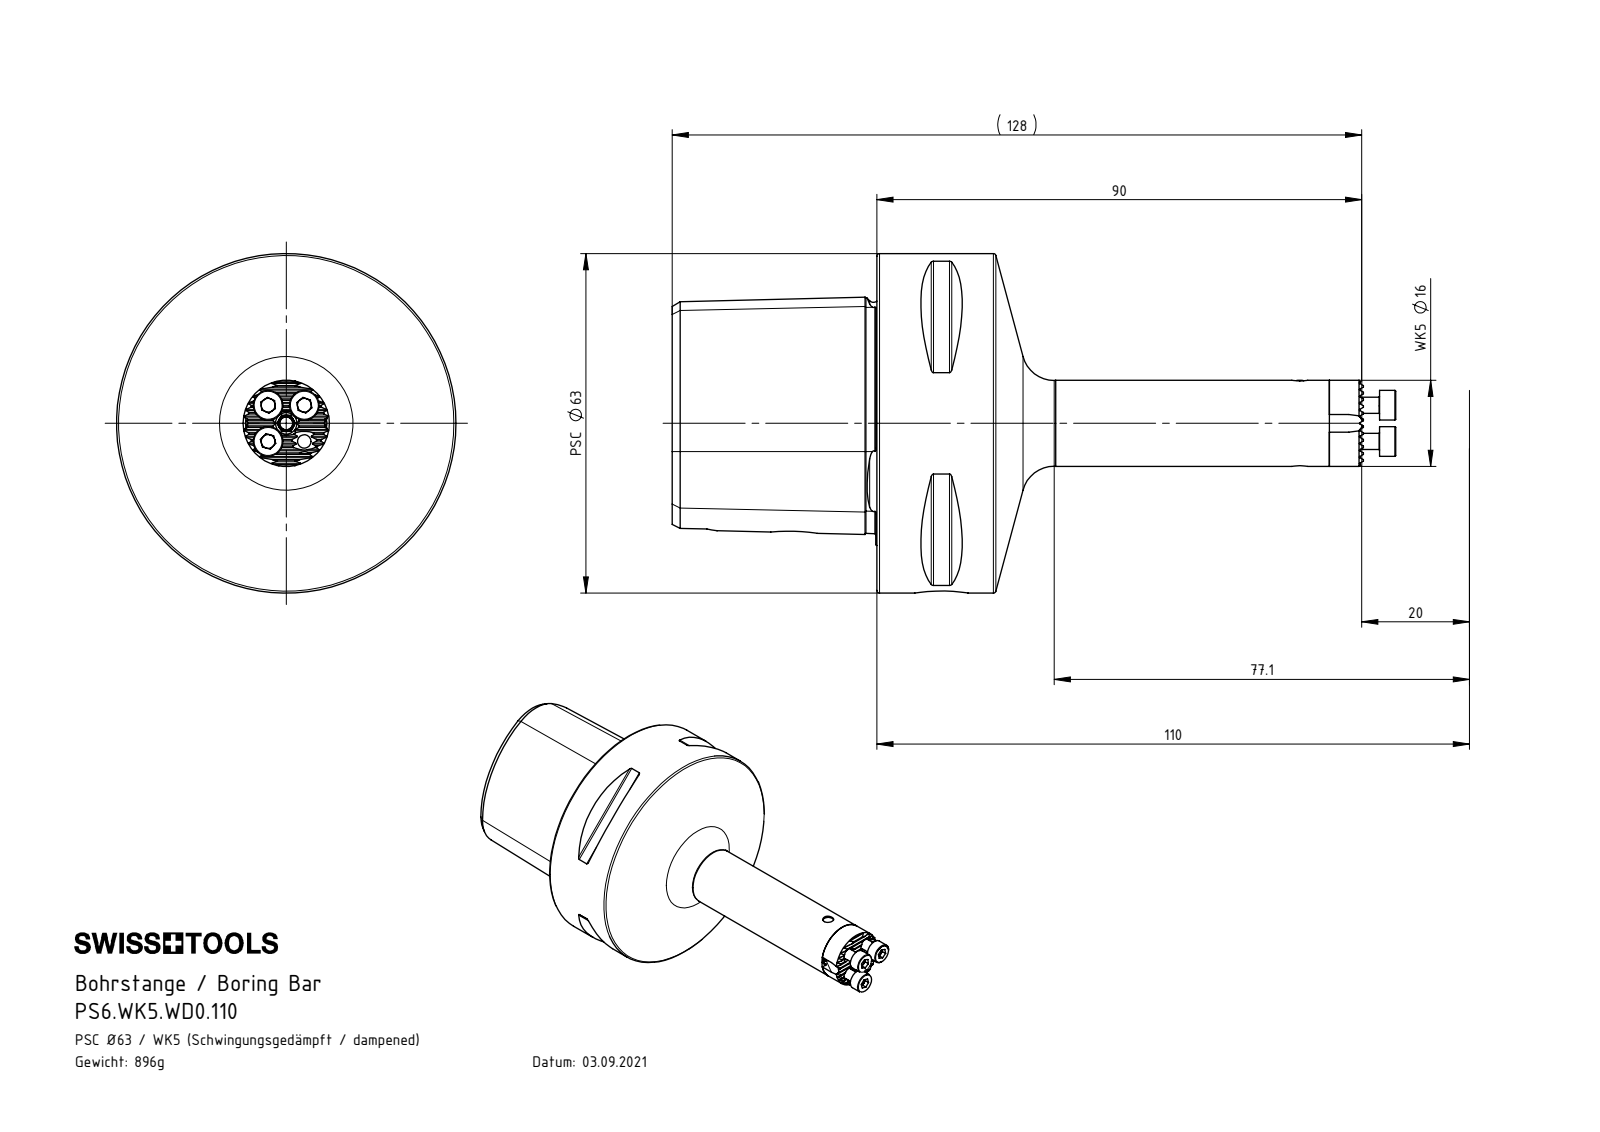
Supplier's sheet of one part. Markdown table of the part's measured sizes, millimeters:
| quantity | value |
| --- | --- |
| part name | PS6.WK5.WD0.110; DIN 3771 - 5x2.5; DIN 3771 - 4x1; WD0-BG1.013.040 (+8 more) |
| STEP written by | SolidWorks 2017 (AUTOMOTIVE_DESIGN) |
| units | millimeters |
| bodies | 18 solids, 480 faces (217 planar, 106 cylindrical, 157 other) |
| overall size | 134.3 × 63 × 63 |
| volume | 114 607 mm³ |
| surface area | 32 270 mm² |
| round holes (diameter × count) | 2.5 × 7, 2 × 3, 3 × 2, 10 × 2, 3.3 × 1, 4 × 1, 4.5 × 1, 5.4 × 1, 6 × 1, 8.1 × 1, 13.2 × 1, 18 × 1 |
| round bosses / shafts (diameter × count) | 3 × 5, 5.5 × 3, 63 × 1, 16 × 1, 13 × 1, 12.6 × 1, 12 × 1, 10.8 × 1 |
| partial cylindrical surfaces (radius × count) | 0.12 × 13, 0.5 × 8, 1.65 × 4, 6 × 1 |
| main face-to-face distances | 38, 24.89, 27, 11, 55.8, 4.5, 34.9, 3, 37.8, 10.8 |
| hole center spacings | 4.75, 6.72, 9.5, 7.5, 13.35, 15.9, 23.4, 27.5 |
